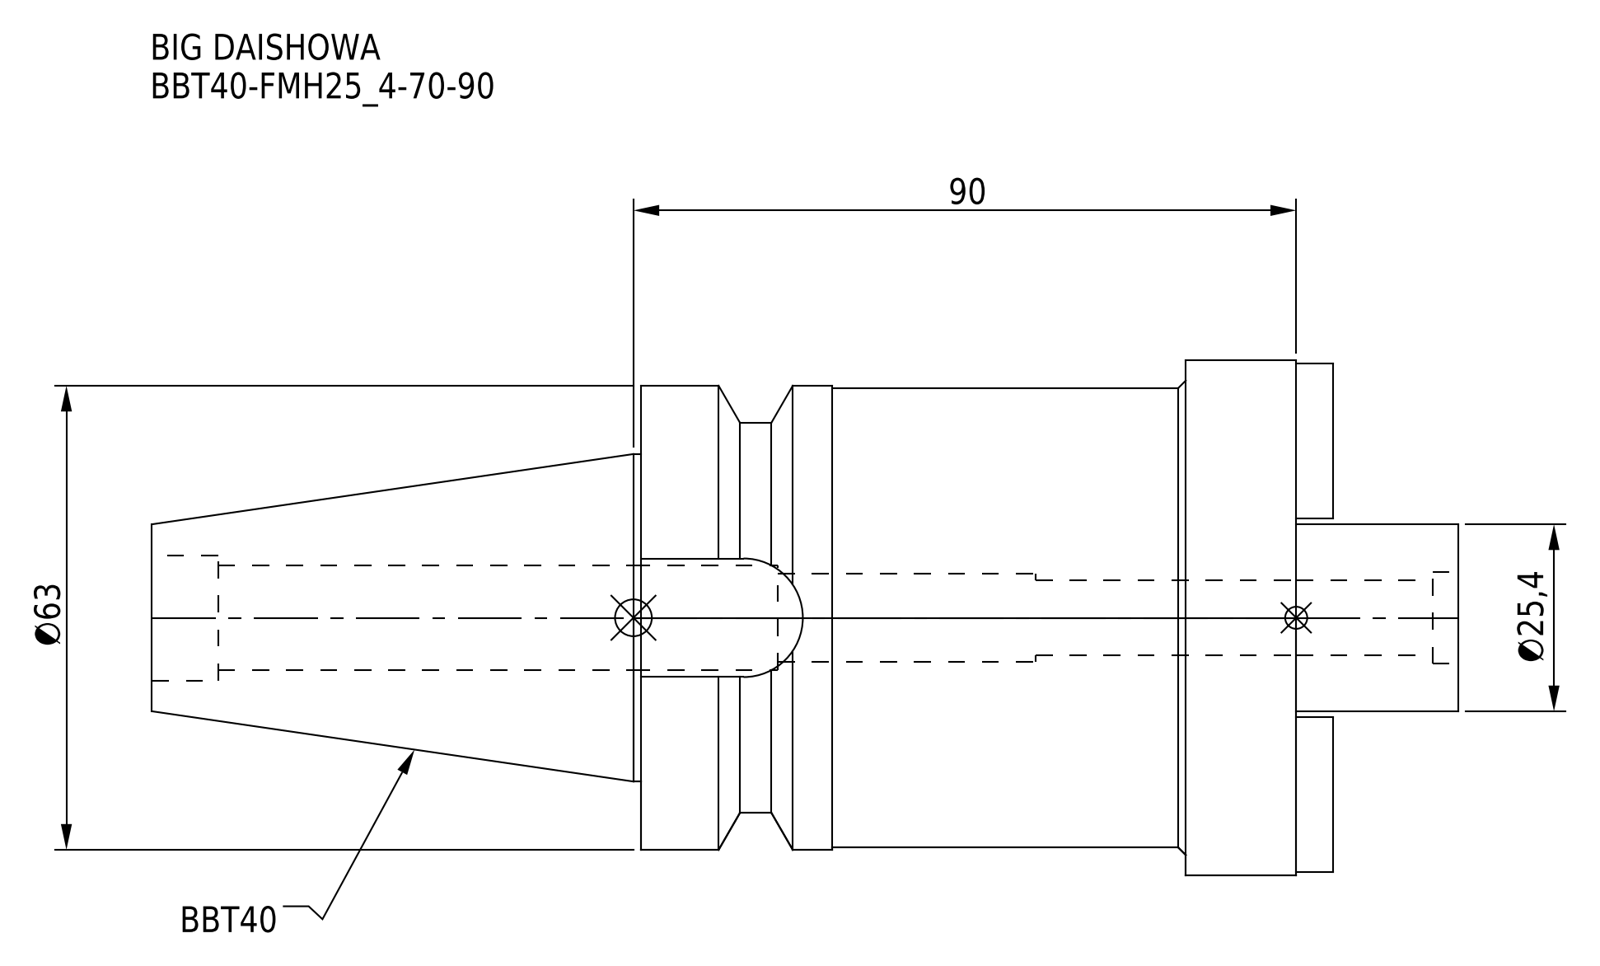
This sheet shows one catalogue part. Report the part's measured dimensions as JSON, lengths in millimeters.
{"part_name": "BBT40-FMH25_4-70-90", "step_written_by": "CREO PARAMETRIC BY PTC INC, 2016380 (AUTOMOTIVE_DESIGN)", "units": "millimeters", "bodies": {"solids": 1, "faces": 64, "planar": 26, "cylindrical": 30, "other": 8}, "overall_size": [177.4, 70, 70], "volume_mm3": 330425, "surface_area_mm2": 42252, "round_holes": [[10.25, 1], [12, 1], [12.5, 1], [14.2, 1], [17, 1]], "round_bosses_or_shafts": [[70, 1], [63, 1], [62.4, 1], [53, 1], [44.45, 1], [25.4, 1]], "partial_cylinders_radius": [[8.05, 1]], "face_to_face_distances": [89, 15, 74, 17.75, 27.25, 111, 5, 20, 94, 17]}
